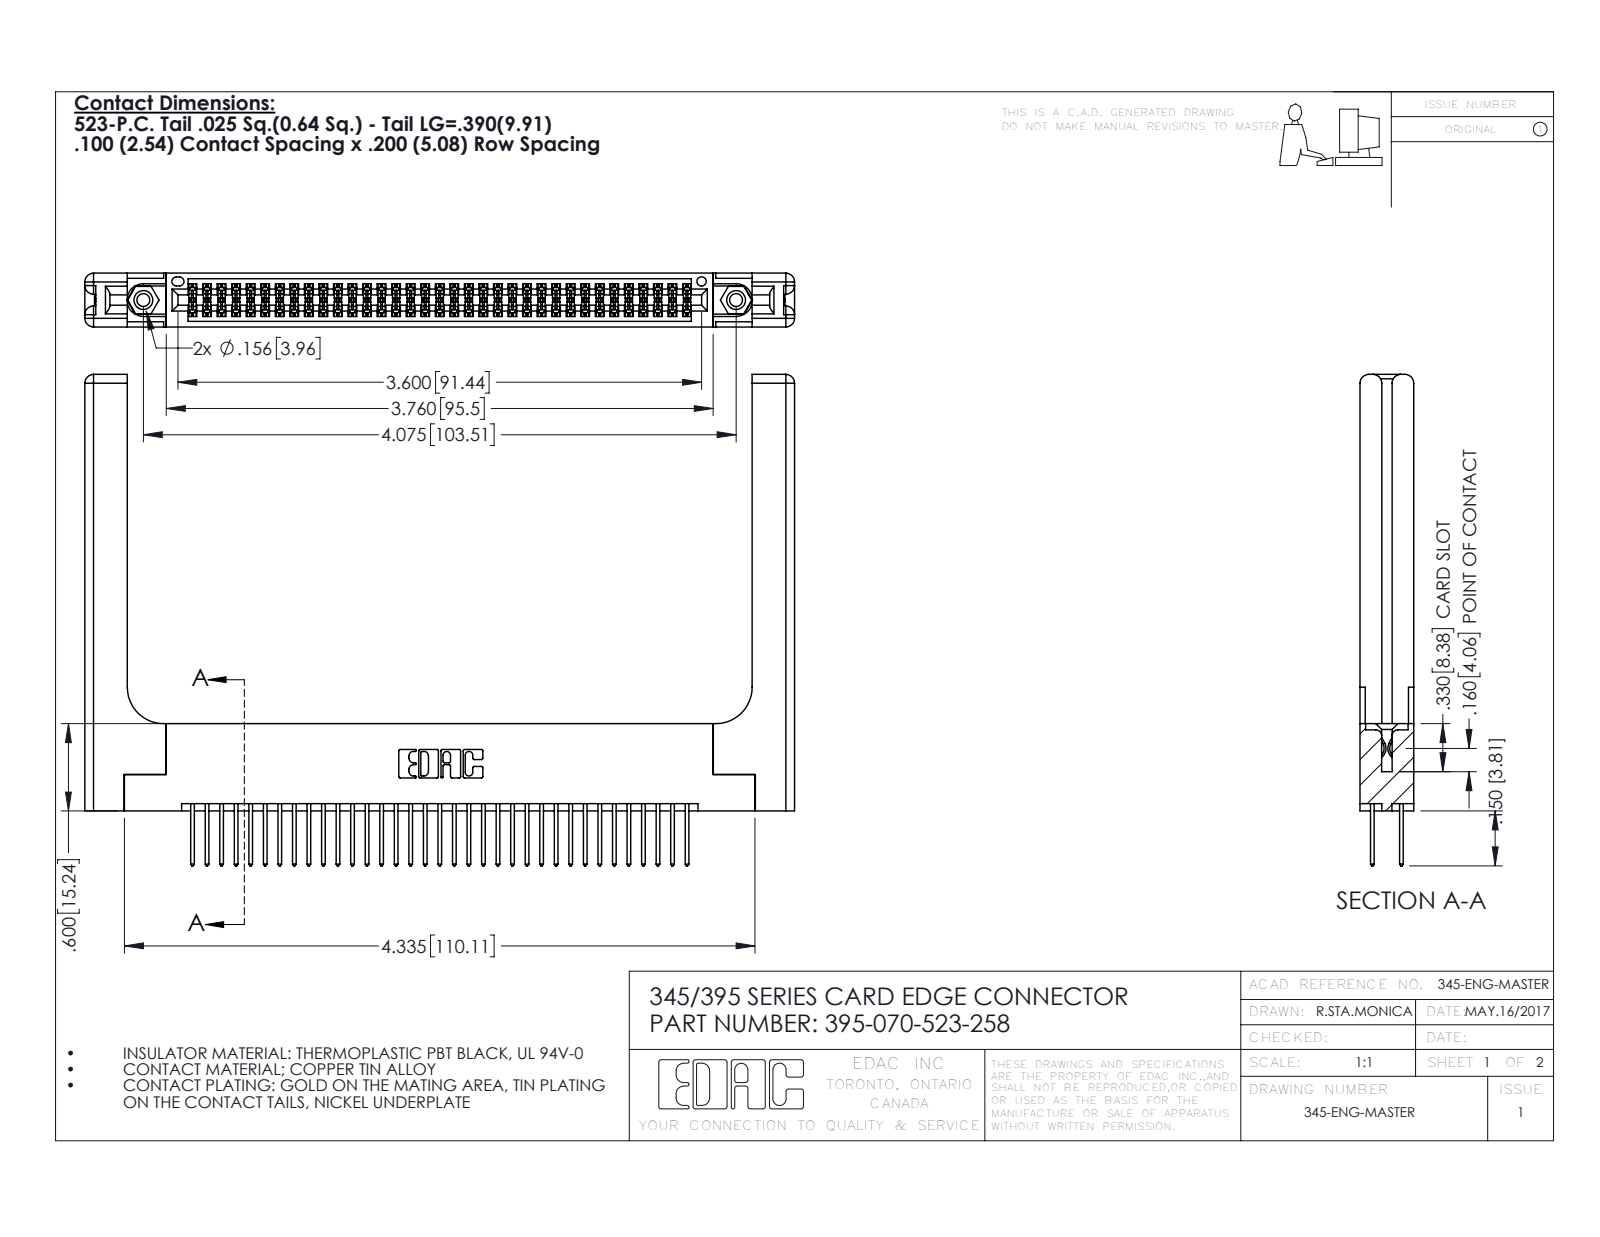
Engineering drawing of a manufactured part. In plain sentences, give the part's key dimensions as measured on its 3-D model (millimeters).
The part is named "345-292-001_345-293-123; 345-250-001_345-250-001-102; 395-070-523-258; 345 Part_Flush Mounting Lugs - 0.156 Dia-TH (+1 more)". Its 3-D file was written by "SolidWorks 2016 (CONFIG_CONTROL_DESIGN)". It is 75 solids with 3882 faces: 2538 planar, 1284 cylindrical and 60 other. Overall it measures 123.9 by 85.8 by 9.4 millimeters. Its volume is 20 600 cubic millimeters and its surface area 23 480 square millimeters. Round holes: 2 of diameter 2.3, 2 of diameter 3.2, 2 of diameter 4, 1 of diameter 1.6. Round bosses or shafts: 2 of diameter 3.9. Partial cylindrical surfaces (rounded edges, fillets, slot ends): 105 of radius 0.2, 70 of radius 0.3, 22 of radius 0.3, 16 of radius 1.5, 6 of radius 0.2, 6 of radius 0.8, 3 of radius 0.7, 2 of radius 0.4. The main face-to-face distances are 1.8, 7.6, 9.4, 5.1, 2.5, 6.9, 0.6, 5.7, 3.8, 3.8. The hole center spacings are 6.9, 97.5, 103.5.
